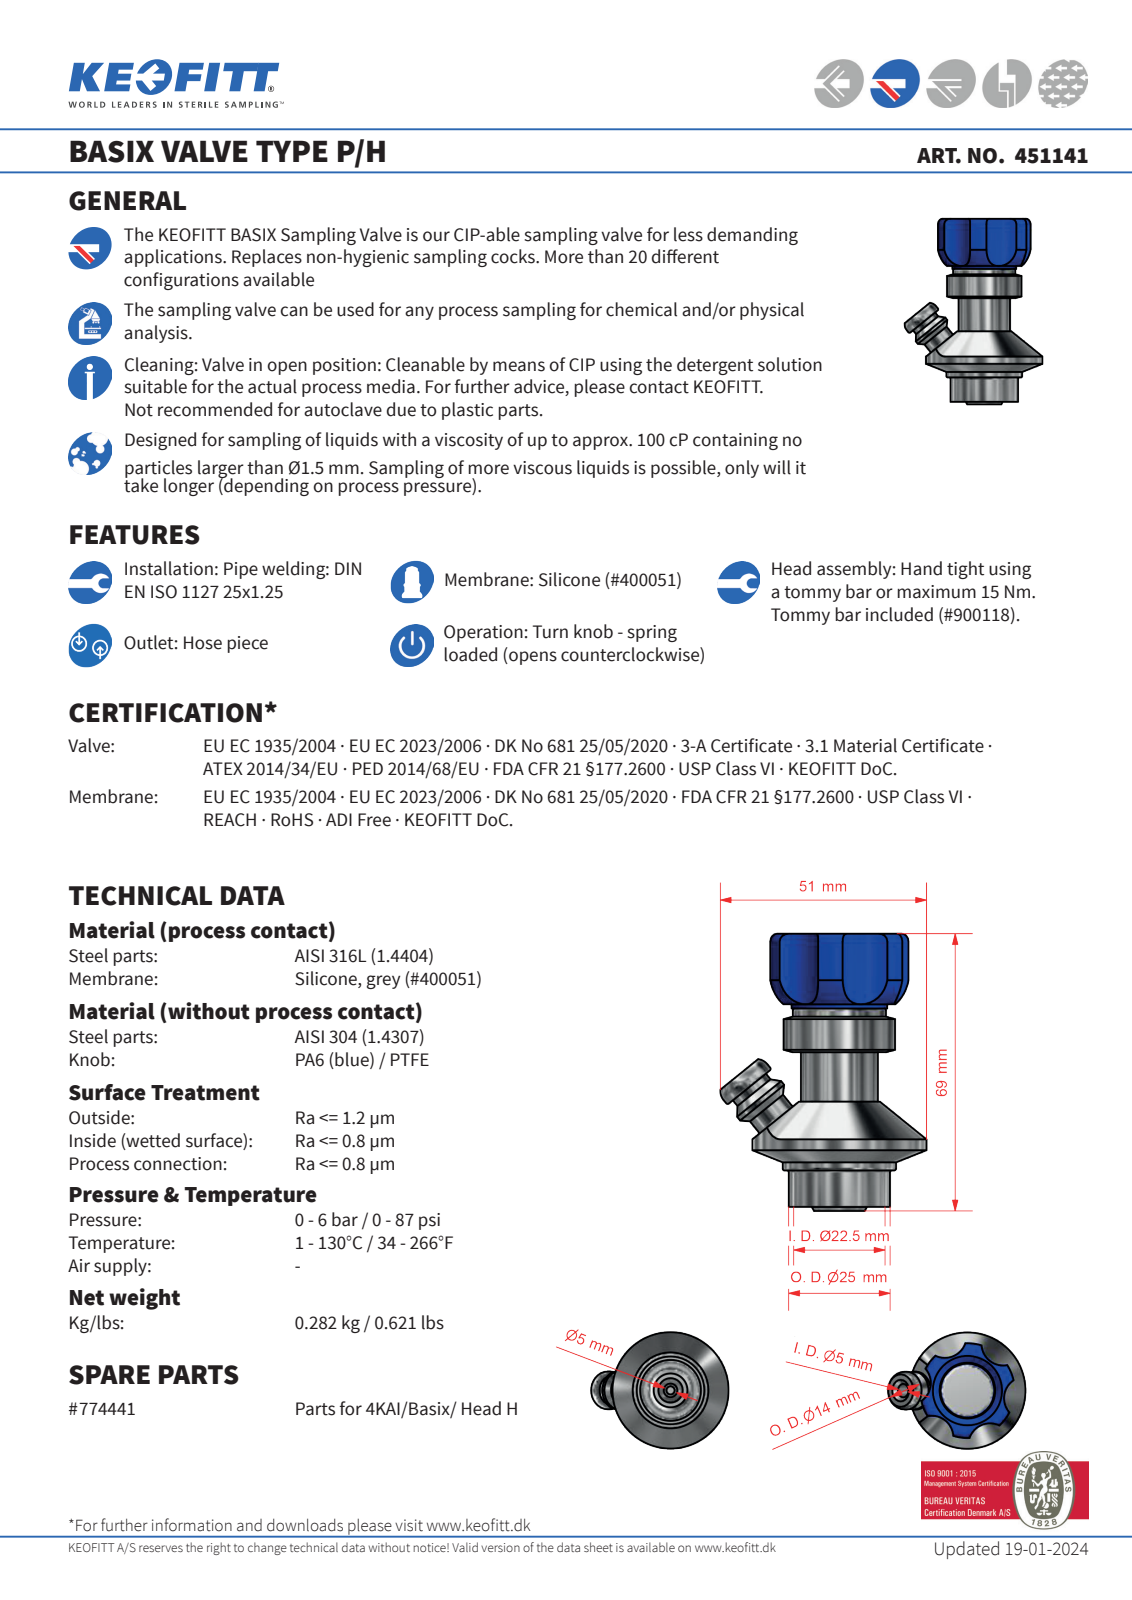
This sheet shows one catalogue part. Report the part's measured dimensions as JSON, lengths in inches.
{"part_name": "451141", "step_written_by": "Autodesk Inventor 2020 (AUTOMOTIVE_DESIGN)", "units": "inches", "bodies": {"solids": 1, "faces": 121, "planar": 27, "cylindrical": 48, "other": 46}, "overall_size": [2.697, 2.004, 1.693], "volume_in3": 2.604, "surface_area_in2": 20, "round_holes": [[0.197, 2], [0.238, 1], [0.65, 1], [0.728, 1], [0.732, 1], [0.772, 1], [0.811, 1], [0.886, 1]], "round_bosses_or_shafts": [[0.551, 2], [1.693, 1], [1.102, 1], [1.083, 1], [0.984, 1], [0.929, 1], [0.906, 1], [0.787, 1]], "partial_cylinders_radius": [[0.315, 8], [0.213, 1], [0.689, 1]], "face_to_face_distances": [0.079, 0.687, 0.041, 0.728, 2.579, 0.036, 0.723, 0.425, 0.43, 0.466]}
